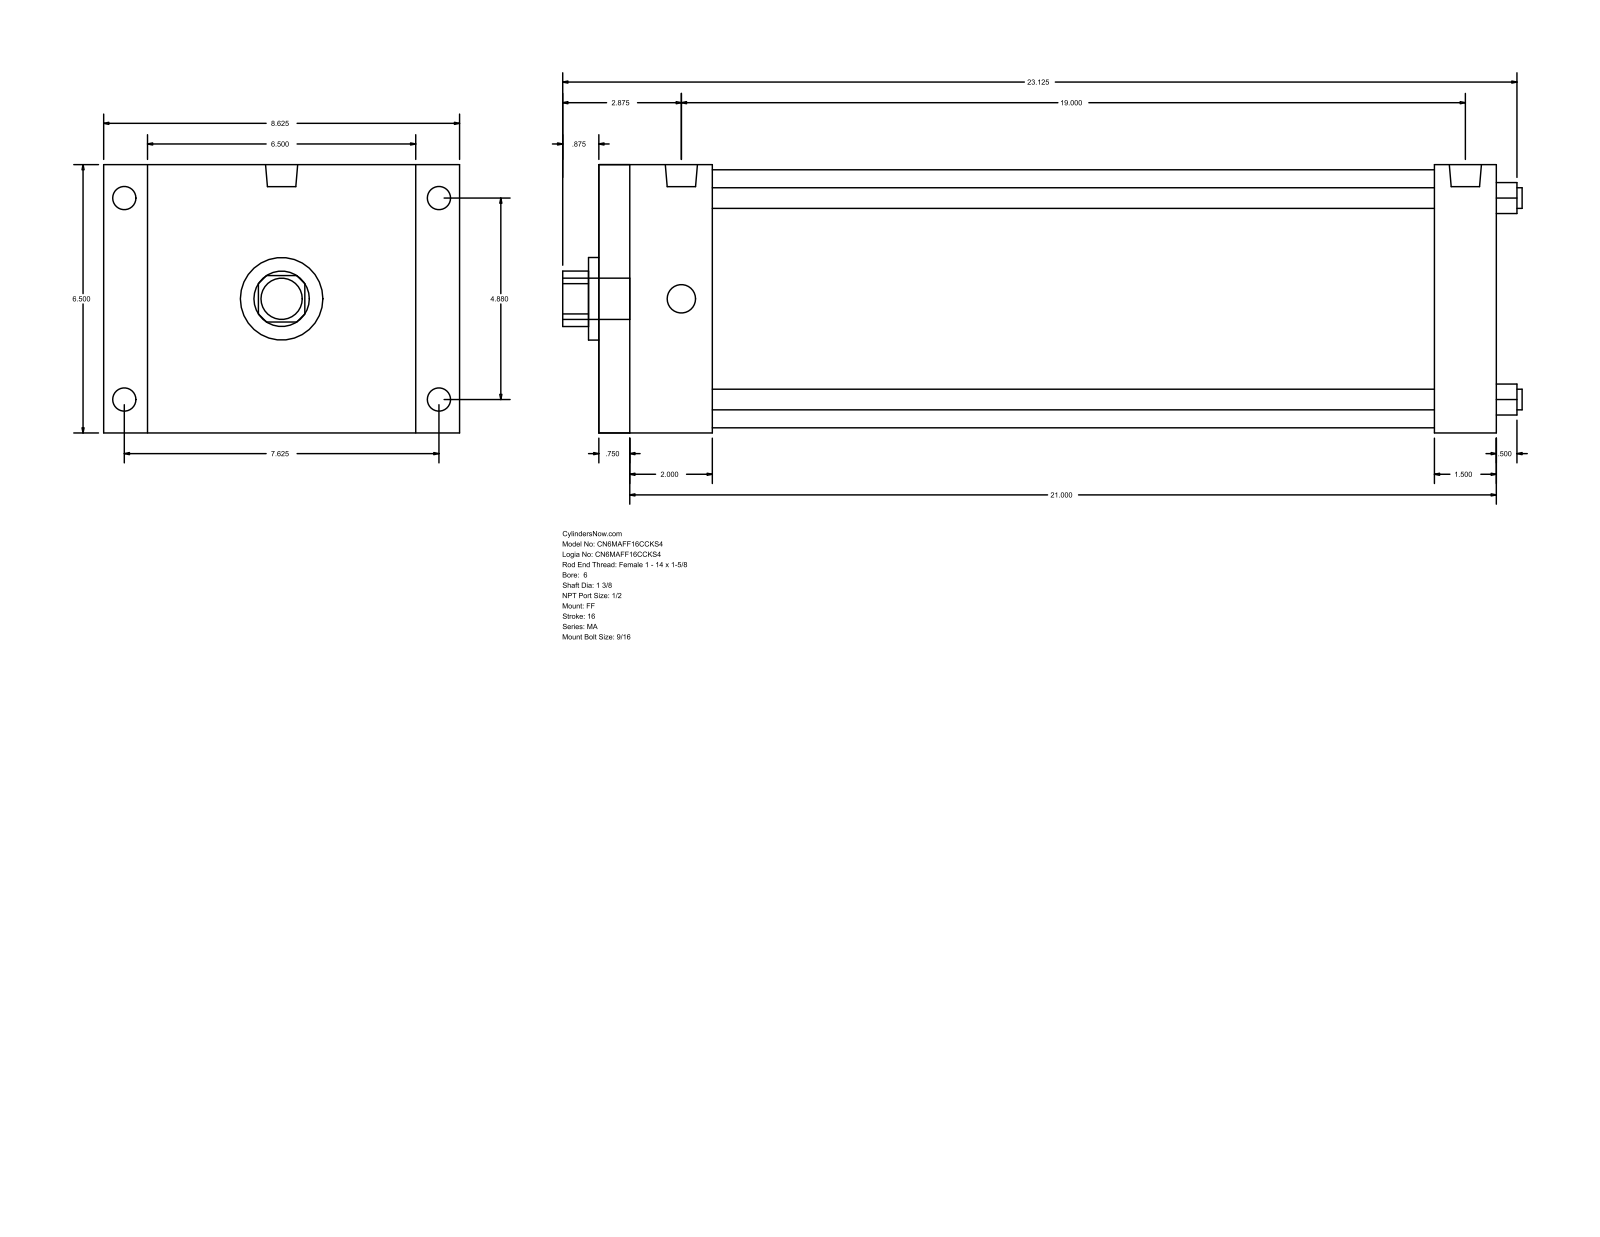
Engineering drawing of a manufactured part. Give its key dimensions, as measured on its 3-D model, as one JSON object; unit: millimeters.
{"part_name": "MA_FF__0600_1.375", "step_written_by": "GSSL Pune (CONFIG_CONTROL_DESIGN)", "units": "millimeters", "bodies": {"solids": 0, "faces": 92, "planar": 64, "cylindrical": 28, "other": 0}, "overall_size": [590.55, 219.07, 165.1], "round_holes": [[12.7, 4], [34.92, 1], [50.8, 1], [158.75, 1]], "round_bosses_or_shafts": [[17.46, 4], [14.29, 4], [19.77, 2], [25.4, 1]], "partial_cylinders_radius": [[17.06, 1]], "face_to_face_distances": [165.1, 552.44, 15.87, 536.57, 50.8, 498.48, 66.67, 485.77, 514.35, 447.68], "hole_center_spacings": [87.65, 123.96, 175.31]}
